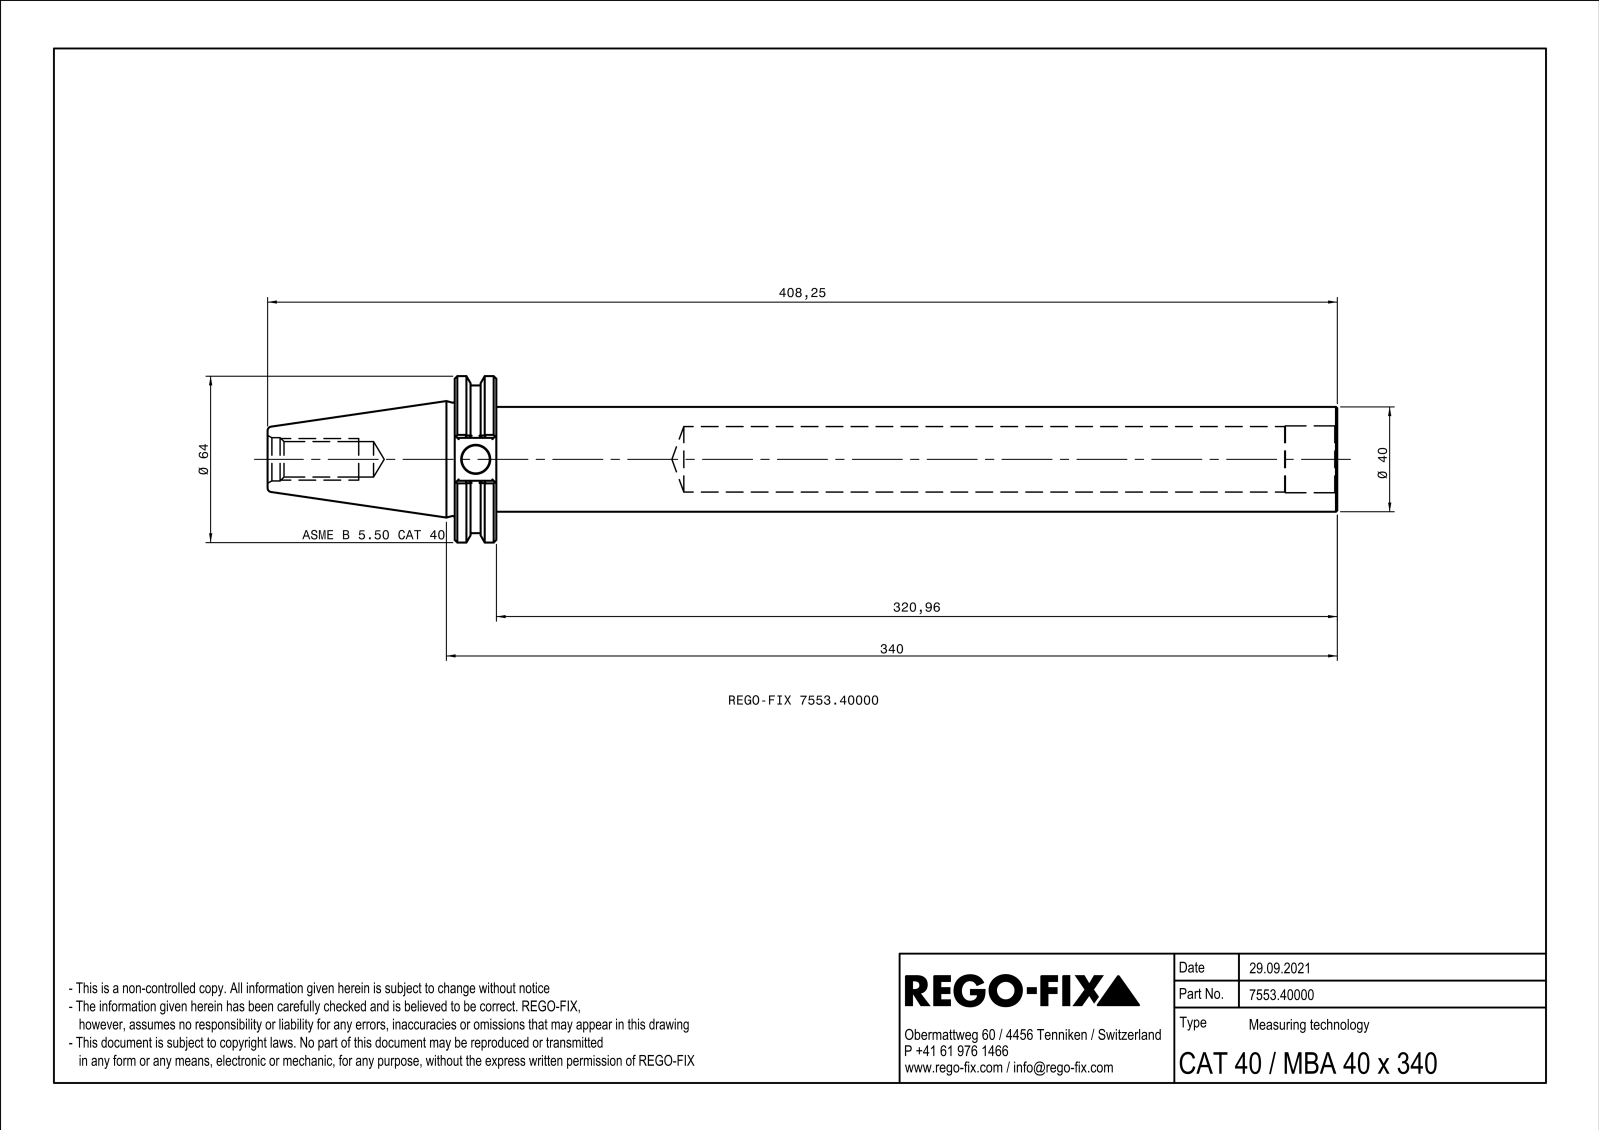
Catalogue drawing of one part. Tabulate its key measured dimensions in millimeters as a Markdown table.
| quantity | value |
| --- | --- |
| part name | NOCUT |
| STEP written by | SIEMENS PLM Software Solid Edge ST10 (AUTOMOTIVE_DESIGN) |
| units | millimeters |
| bodies | 1 solid, 86 faces (30 planar, 18 cylindrical, 38 other) |
| overall size | 408.25 × 63.5 × 60.79 |
| volume | 385 906 mm³ |
| surface area | 78 379 mm² |
| round holes (diameter × count) | 10.7 × 1, 13.53 × 1, 16.5 × 1, 25 × 1, 25.5 × 1 |
| round bosses / shafts (diameter × count) | 63.5 × 1, 56.36 × 1, 40 × 1, 39.4 × 1 |
| partial cylindrical surfaces (radius × count) | 0.5 × 4 |
| main face-to-face distances | 15.87, 320.96, 336.83, 47.33, 16.38, 408.25, 87.29, 71.42, 326.95, 5.99 |
